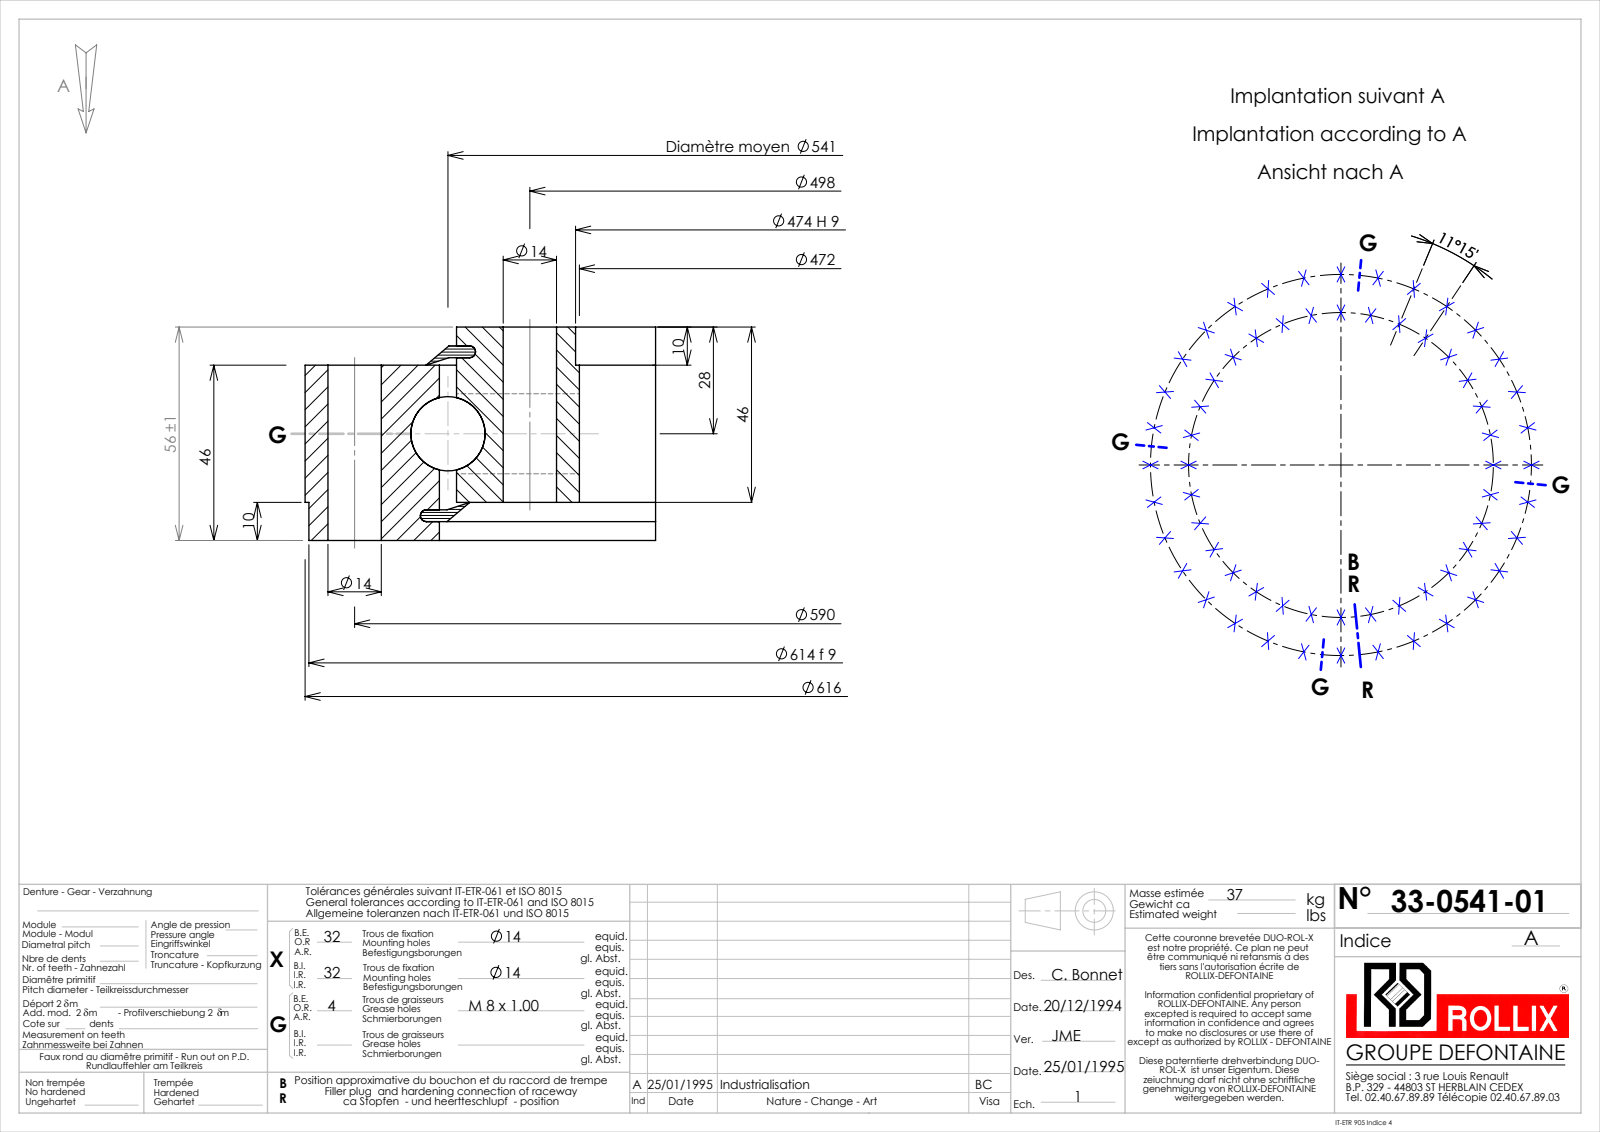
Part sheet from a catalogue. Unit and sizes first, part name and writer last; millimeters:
Units: millimetres
Overall size (bounding box): 632.55 × 632.55 × 56
Round holes (diameter × count): ⌀14 ×64, ⌀7 ×4, ⌀472 ×1, ⌀474 ×1, ⌀545.5 ×1
Round bosses / shafts (diameter × count): ⌀8 ×4, ⌀616 ×1, ⌀614 ×1, ⌀536.5 ×1
Main face-to-face distances: 46, 10, 36, 56, 4.95, 51.05, 5.05, 41.05, 8.05, 47.95
Hole centre spacings: 48.81, 97.16, 190.58, 234.76, 276.68, 315.93, 414.08, 488.44
Volume: 4 516 000 mm³ · Surface area: 814 754 mm²
Bodies: 9 solids, 286 faces (54 planar, 164 cylindrical, 68 other)
Part name (STEP PRODUCT): 33-0541-01
STEP written by: SolidWorks 2016 (CONFIG_CONTROL_DESIGN)
